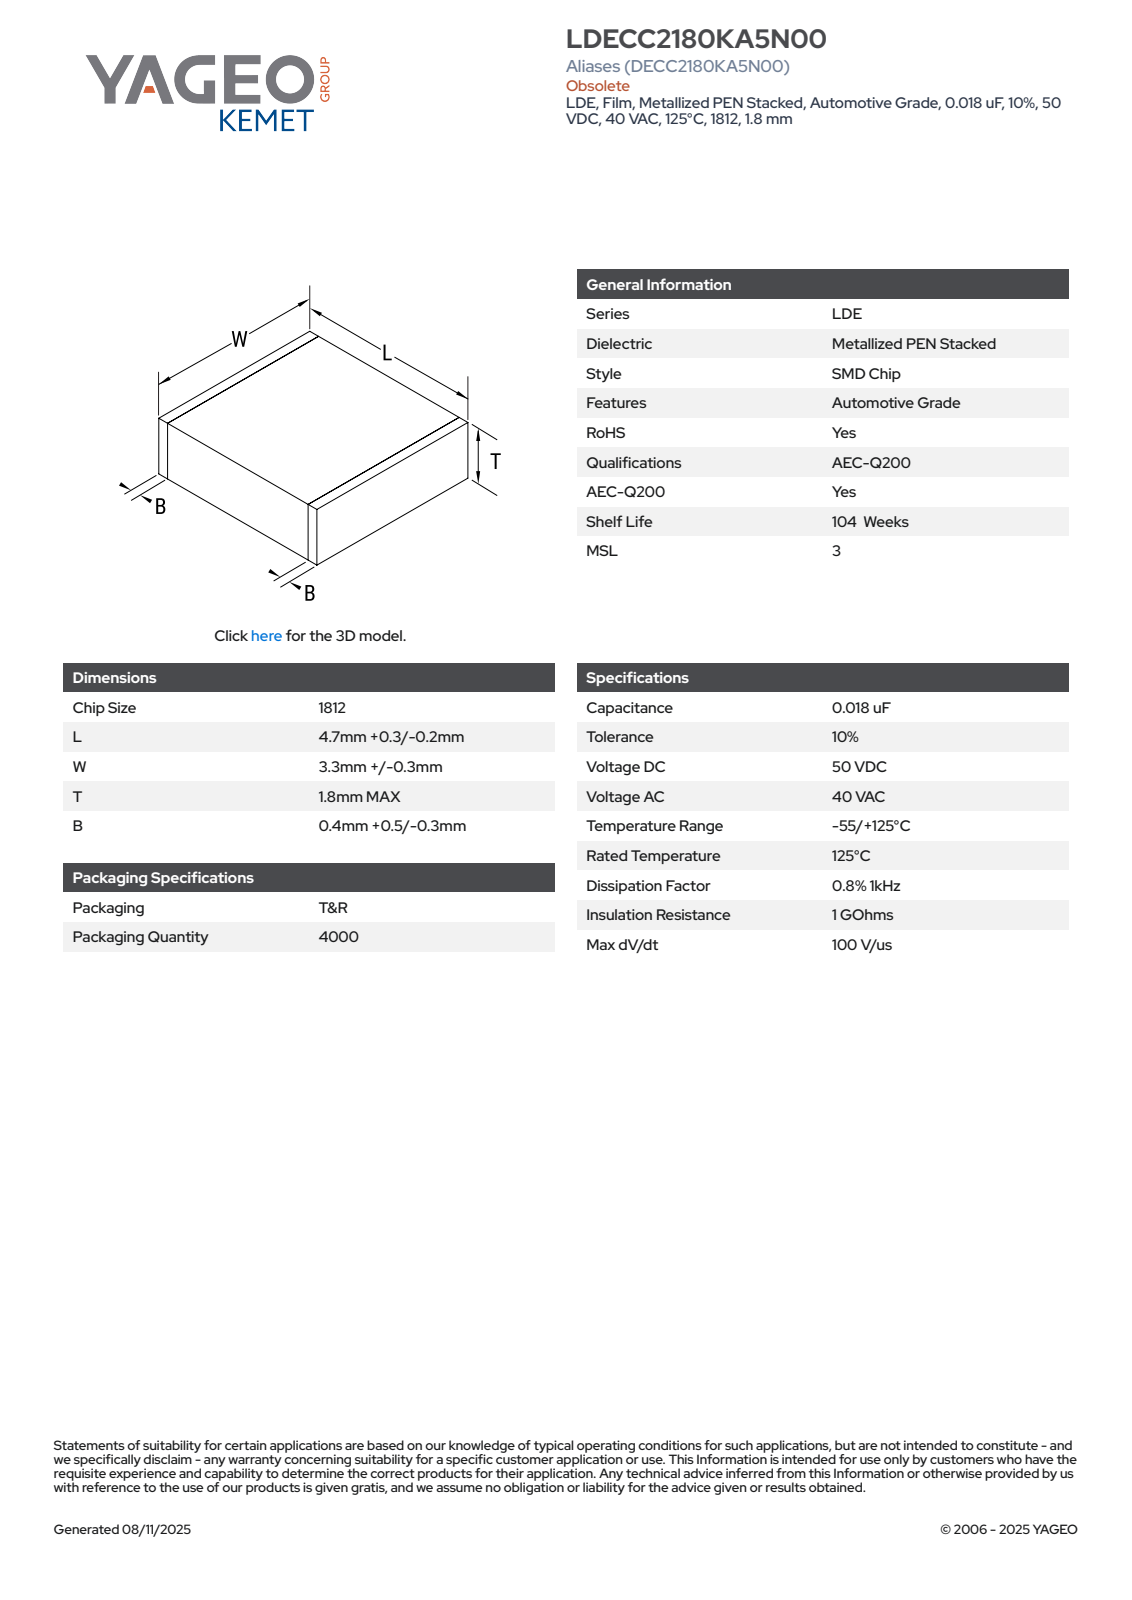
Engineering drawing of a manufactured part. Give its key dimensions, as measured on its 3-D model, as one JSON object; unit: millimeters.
{"part_name": "CFS_LDELDB_1812_L5W3.6T1.8B0.9", "step_written_by": "SolidWorks 2020 (AUTOMOTIVE_DESIGN)", "units": "millimeters", "bodies": {"solids": 4, "faces": 73, "planar": 73, "cylindrical": 0, "other": 0}, "overall_size": [5, 3.6, 1.8], "volume_mm3": 32, "surface_area_mm2": 68, "face_to_face_distances": [1.78, 1.79, 3.58, 5, 3.59, 1.8, 3.6, 0.5, 4.5, 4]}
